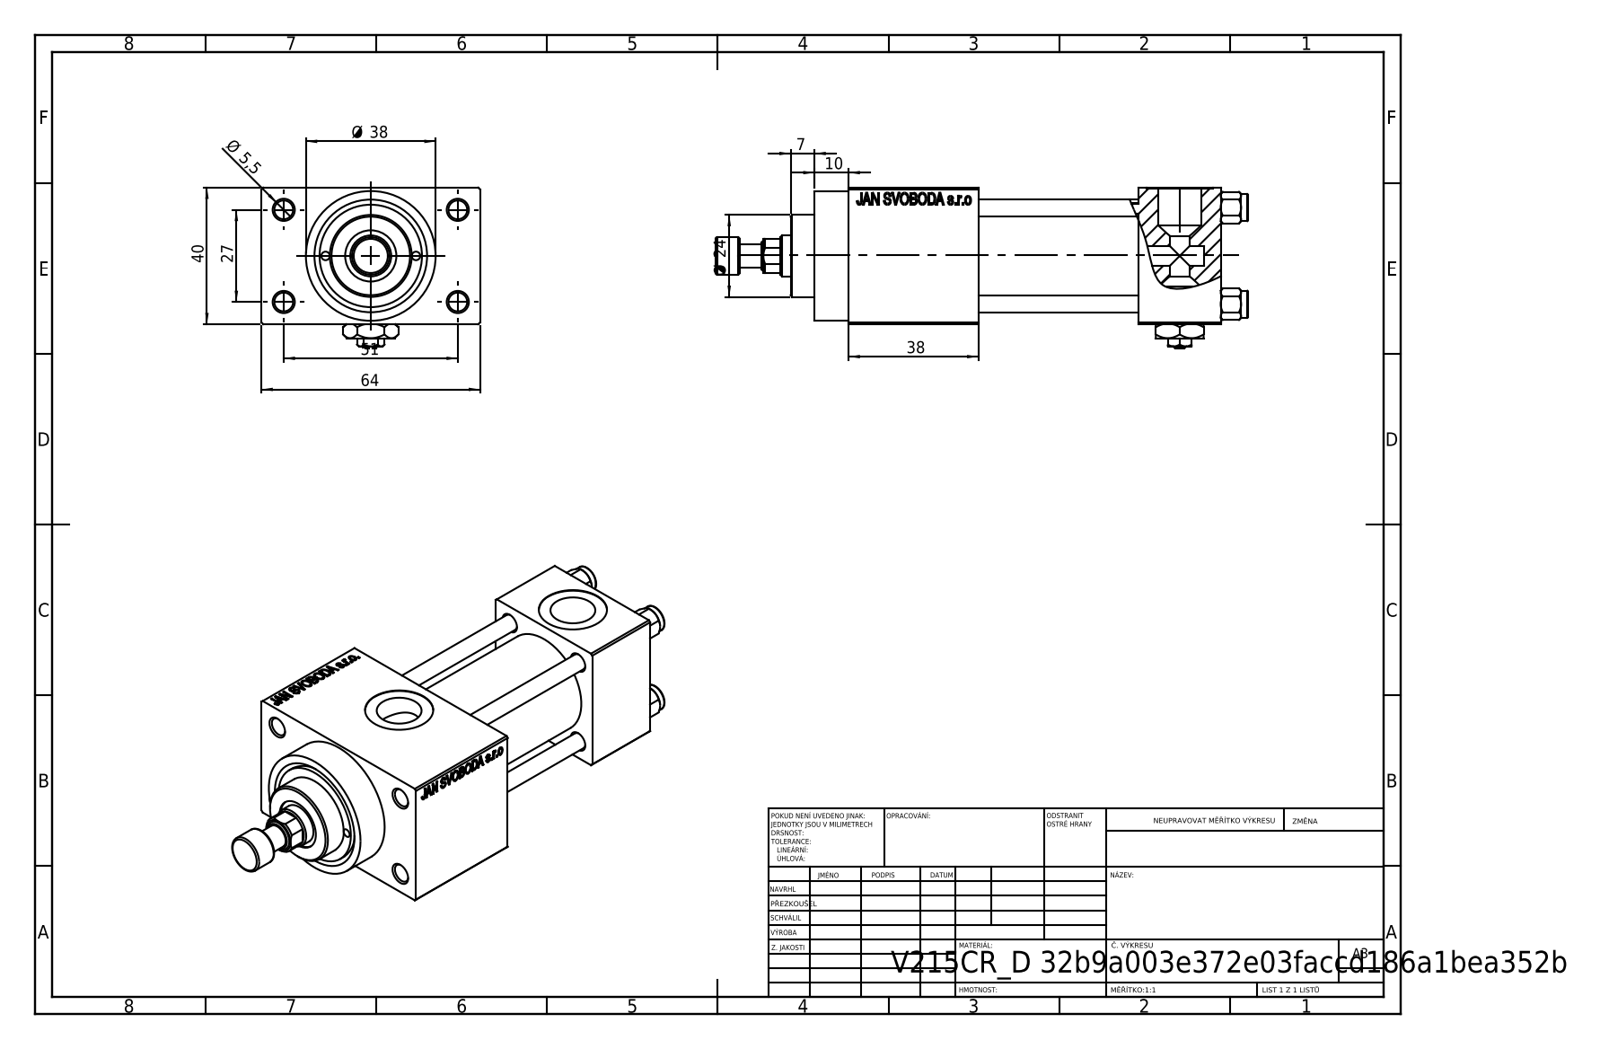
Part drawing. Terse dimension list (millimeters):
name: V215CR_D_TYCINKA; V215CR_D_Body; Zatka_pro_OIL_PORT; V215_VC_A (+3 more)
written by: SolidWorks 2019 (CONFIG_CONTROL_DESIGN)
unit: mm
bodies: 13 solids, 1177 faces (525 planar, 104 cylindrical, 548 other)
size: 156 × 64 × 47
volume: 174 941 mm³; area: 63 367 mm²
holes: 4× ⌀5, 4× ⌀5.5, 3× ⌀20, 2× ⌀2.5, 2× ⌀7, 2× ⌀13.16, 1× ⌀6.5, 1× ⌀12, 1× ⌀15, 1× ⌀25, 1× ⌀30
bosses: 4× ⌀8, 1× ⌀38, 1× ⌀31, 1× ⌀24, 1× ⌀11
face distances: 40, 52, 12, 47, 24, 71, 64, 38, 109, 85
hole spacings: 11.37, 14.18, 18.23, 20.01, 28.3, 28.85, 29.89, 30.84
